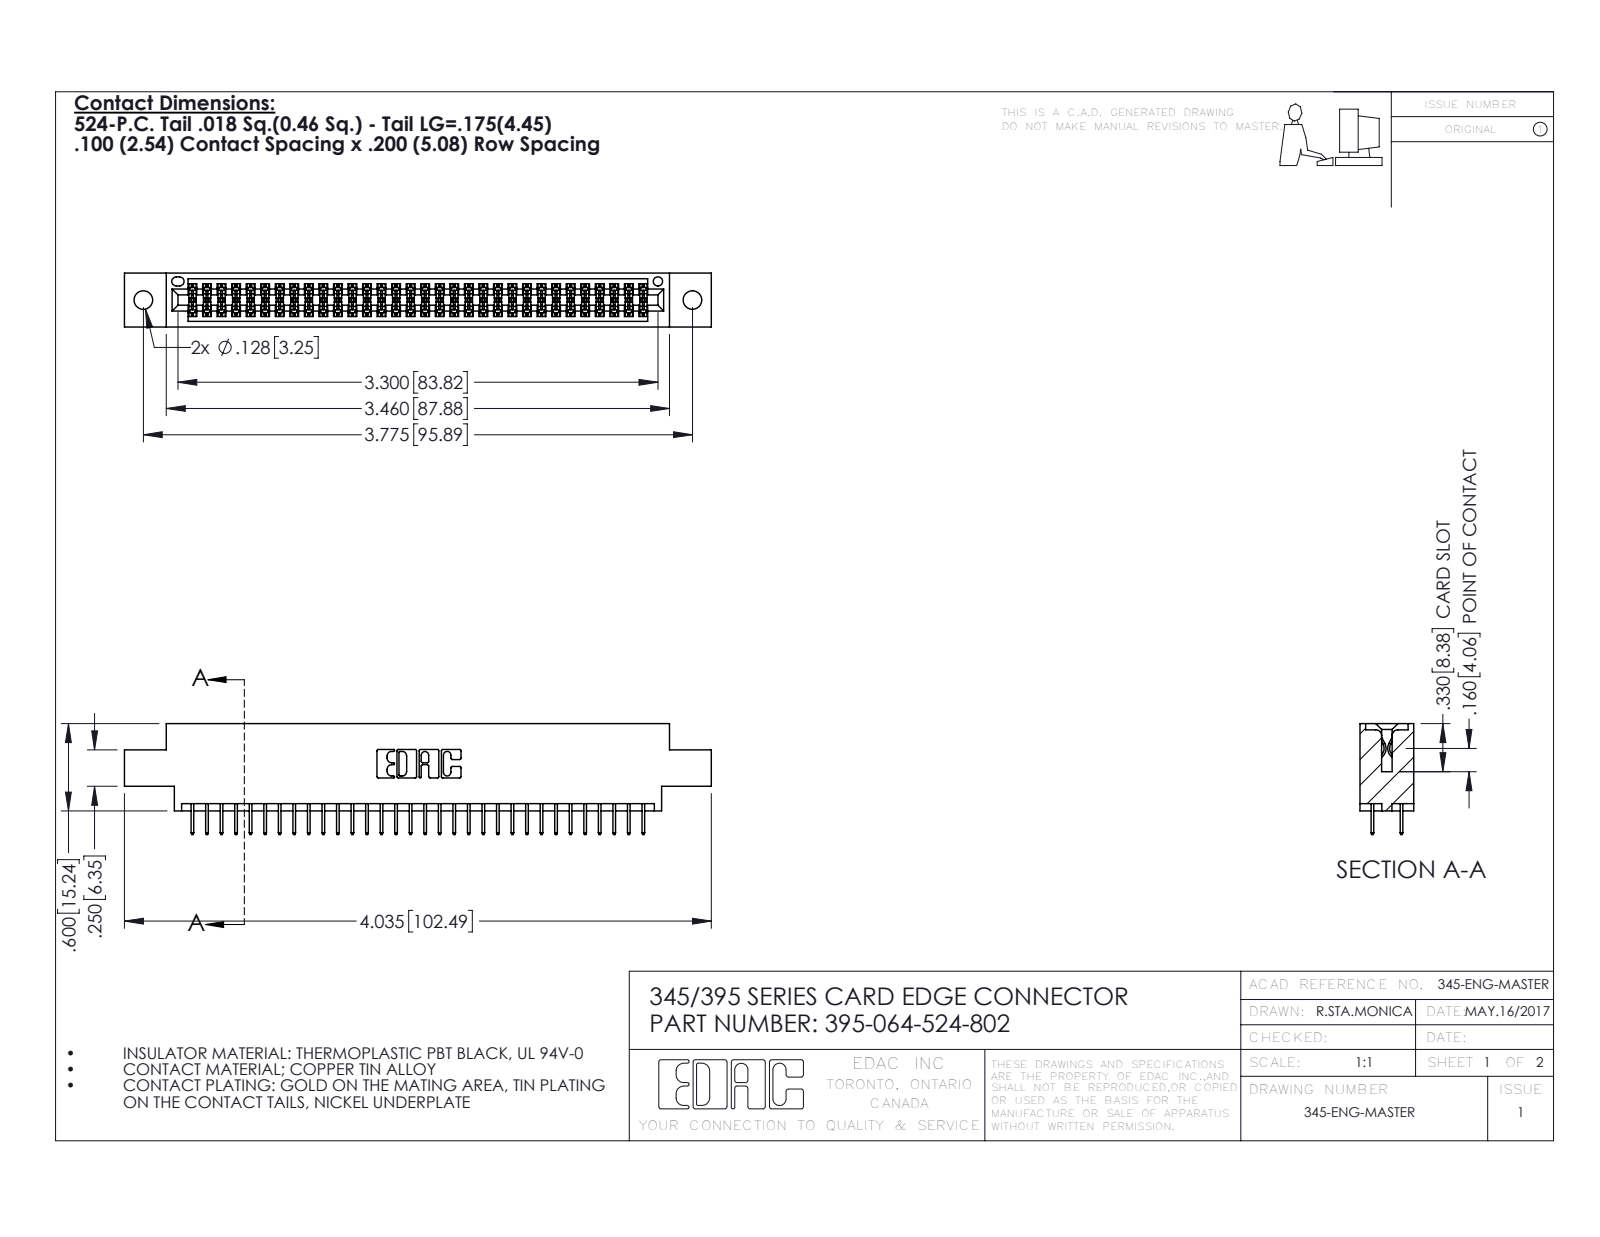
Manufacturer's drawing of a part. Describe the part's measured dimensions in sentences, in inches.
The part is named "345 Part_0.170 Offset - 0.128 Dia; 395-064-524-802; 345-292-001_345-293-124". Its 3-D file was written by "SolidWorks 2016 (CONFIG_CONTROL_DESIGN)". It is 65 solids with 3586 faces: 2580 planar, 1006 cylindrical and 0 other. Overall it measures 4.035 by 0.762 by 0.37 inches. Its volume is 0.587 cubic inches and its surface area 21.14 square inches. Round holes: 2 of diameter 0.128, 1 of diameter 0.064. Partial cylindrical surfaces (rounded edges, fillets, slot ends): 96 of radius 0.006, 22 of radius 0.01, 6 of radius 0.007, 6 of radius 0.031, 3 of radius 0.026, 2 of radius 0.014, 2 of radius 0.019, 2 of radius 0.022. The main face-to-face distances are 0.072, 0.298, 0.37, 0.2, 0.098, 0.272, 0.025, 0.225, 0.175, 0.072. The hole center spacings are 0.27, 3.54, 3.775.
